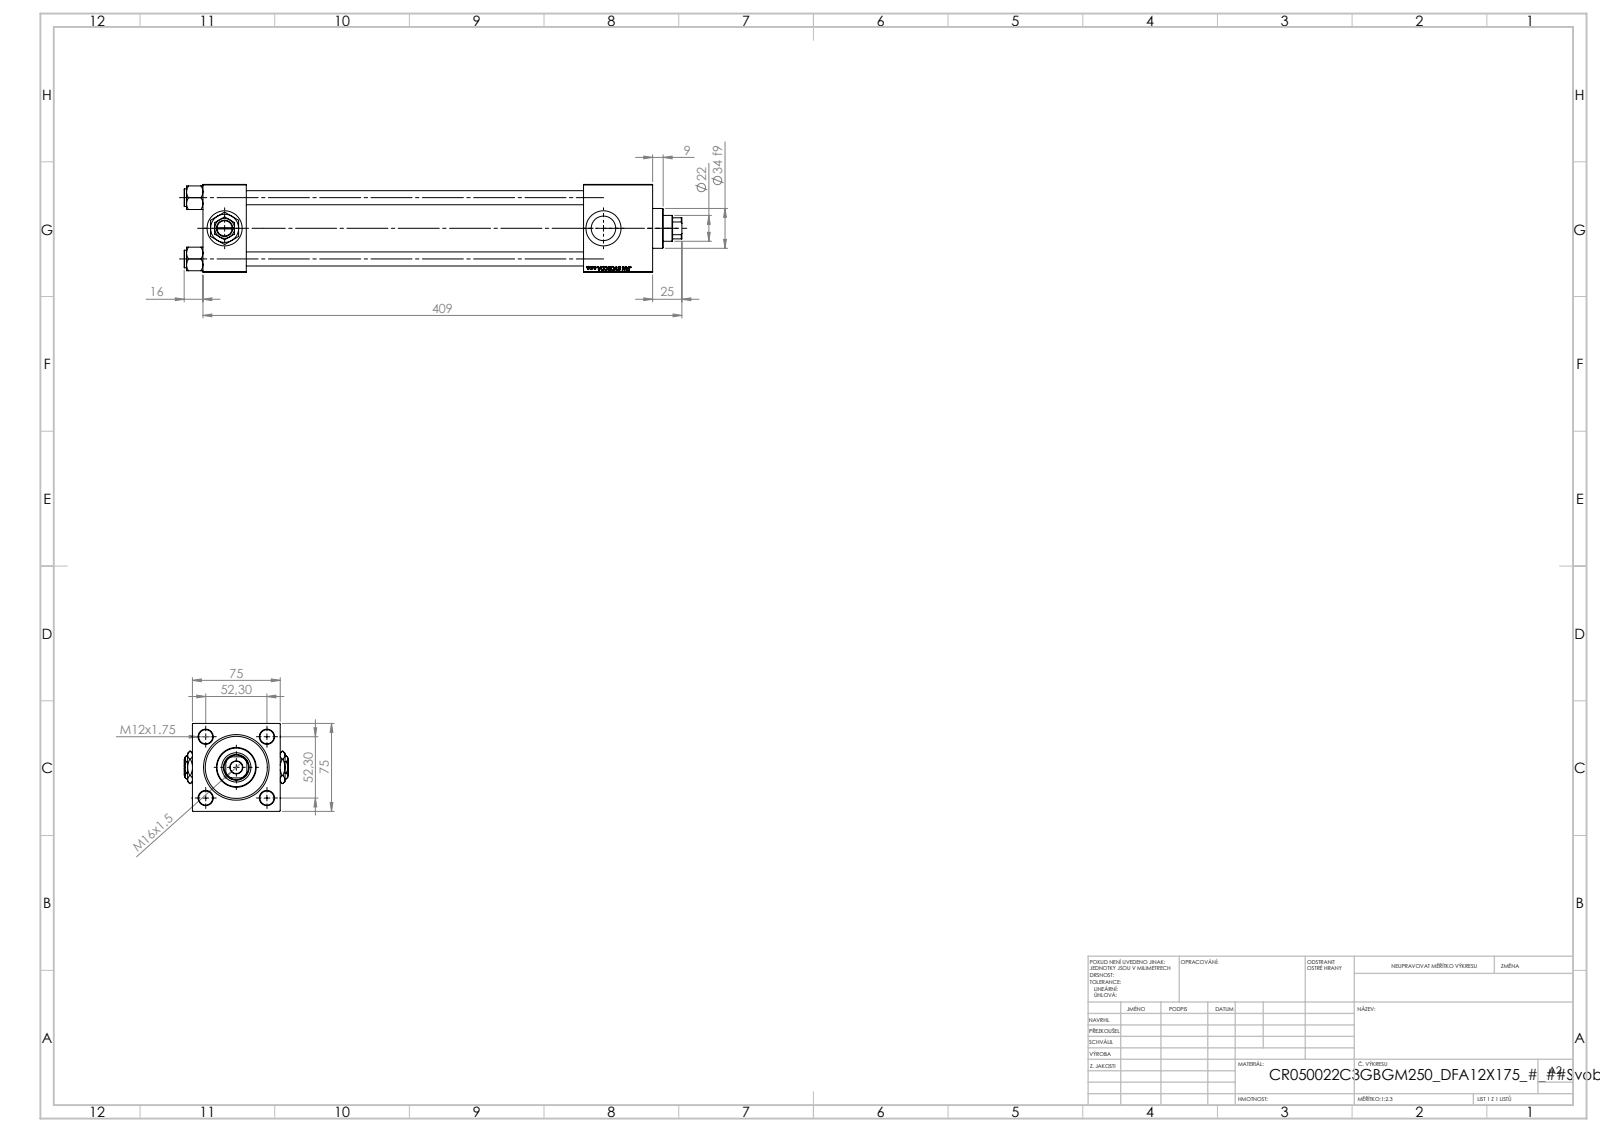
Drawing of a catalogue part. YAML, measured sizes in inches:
part_name: "V215CR_C_TYCINKA; V215CR_VCP_C; Zatka_pro_OIL_PORT; V215_VC_A (+3 more)"
step_written_by: "SolidWorks 2019 (CONFIG_CONTROL_DESIGN)"
units: inches
bodies: {solids: 14, faces: 1282, planar: 585, cylindrical: 107, other: 590}
overall_size: [16.732, 3.504, 2.953]
volume: 59.07
surface_area: 439.2
round_holes:
  - {diameter: 0.472, count: 4}
  - {diameter: 0.276, count: 2}
  - {diameter: 0.825, count: 2}
  - {diameter: 1.181, count: 2}
  - {diameter: 0.413, count: 1}
  - {diameter: 0.866, count: 1}
  - {diameter: 0.984, count: 1}
  - {diameter: 1.614, count: 1}
  - {diameter: 1.969, count: 1}
  - {diameter: 2.087, count: 1}
round_bosses_or_shafts:
  - {diameter: 0.591, count: 4}
  - {diameter: 2.205, count: 1}
  - {diameter: 1.339, count: 1}
  - {diameter: 1.102, count: 1}
  - {diameter: 0.945, count: 1}
  - {diameter: 0.472, count: 1}
  - {diameter: 0.394, count: 1}
partial_cylinders:
  - {radius: 0.384, count: 1}
  - {radius: 0.413, count: 1}
face_to_face_distances: [2.953, 1.457, 15.118, 13.661, 12.795, 11.339, 2.323, 13.988, 12.531, 1.193]
hole_center_spacings: [1.456, 2.059, 2.912, 12.736]
